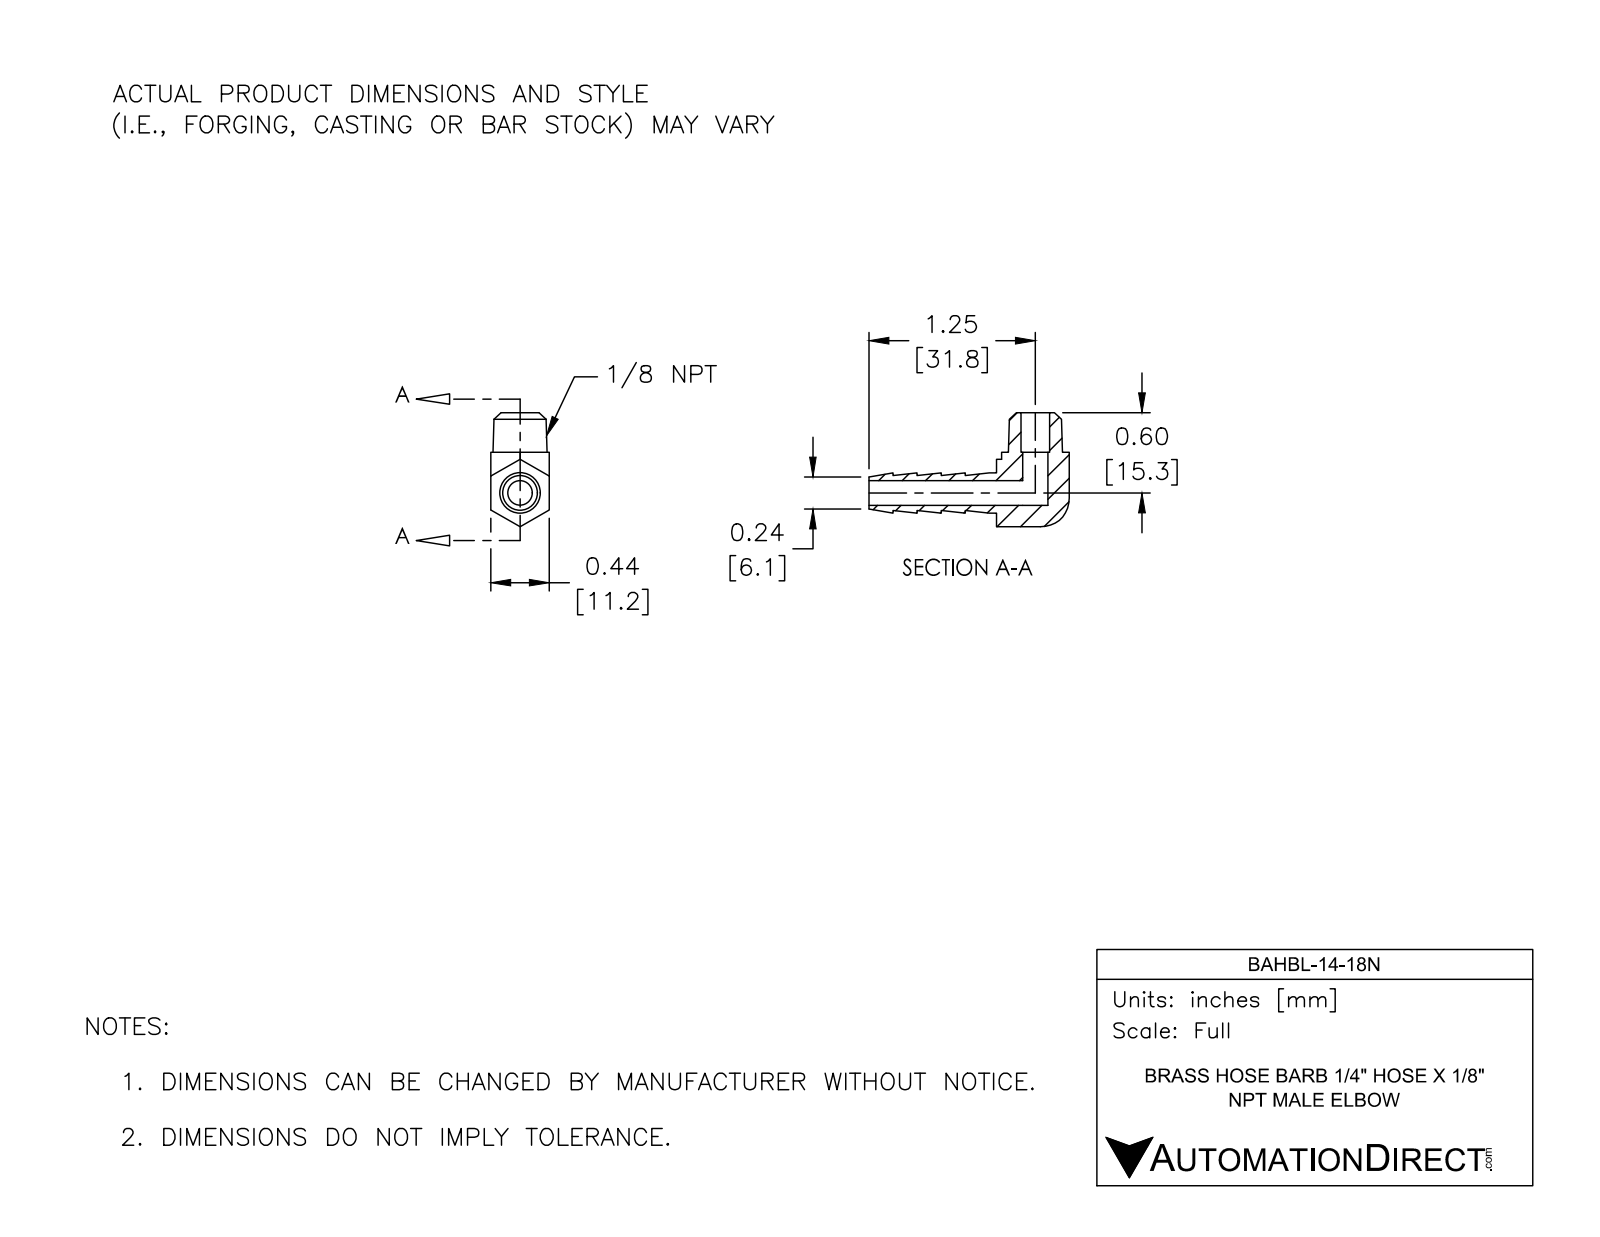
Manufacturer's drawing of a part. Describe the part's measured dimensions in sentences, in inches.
The part is named "BAHBL-14-18N". Its 3-D file was written by "SolidWorks 2017 (AUTOMOTIVE_DESIGN)". It is 1 solid with 44 faces: 20 planar, 10 cylindrical and 14 other. Overall it measures 1.506 by 0.858 by 0.44 inches. Its volume is 0.139 cubic inches and its surface area 3.504 square inches. Round holes: 1 of diameter 0.185, 1 of diameter 0.19, 1 of diameter 0.215. Round bosses or shafts: 1 of diameter 0.303. Partial cylindrical surfaces (rounded edges, fillets, slot ends): 2 of radius 0.25. The main face-to-face distances are 0.44, 0.181, 0.543, 0.362, 0.398, 0.696, 0.298, 0.959, 0.235, 0.416.
